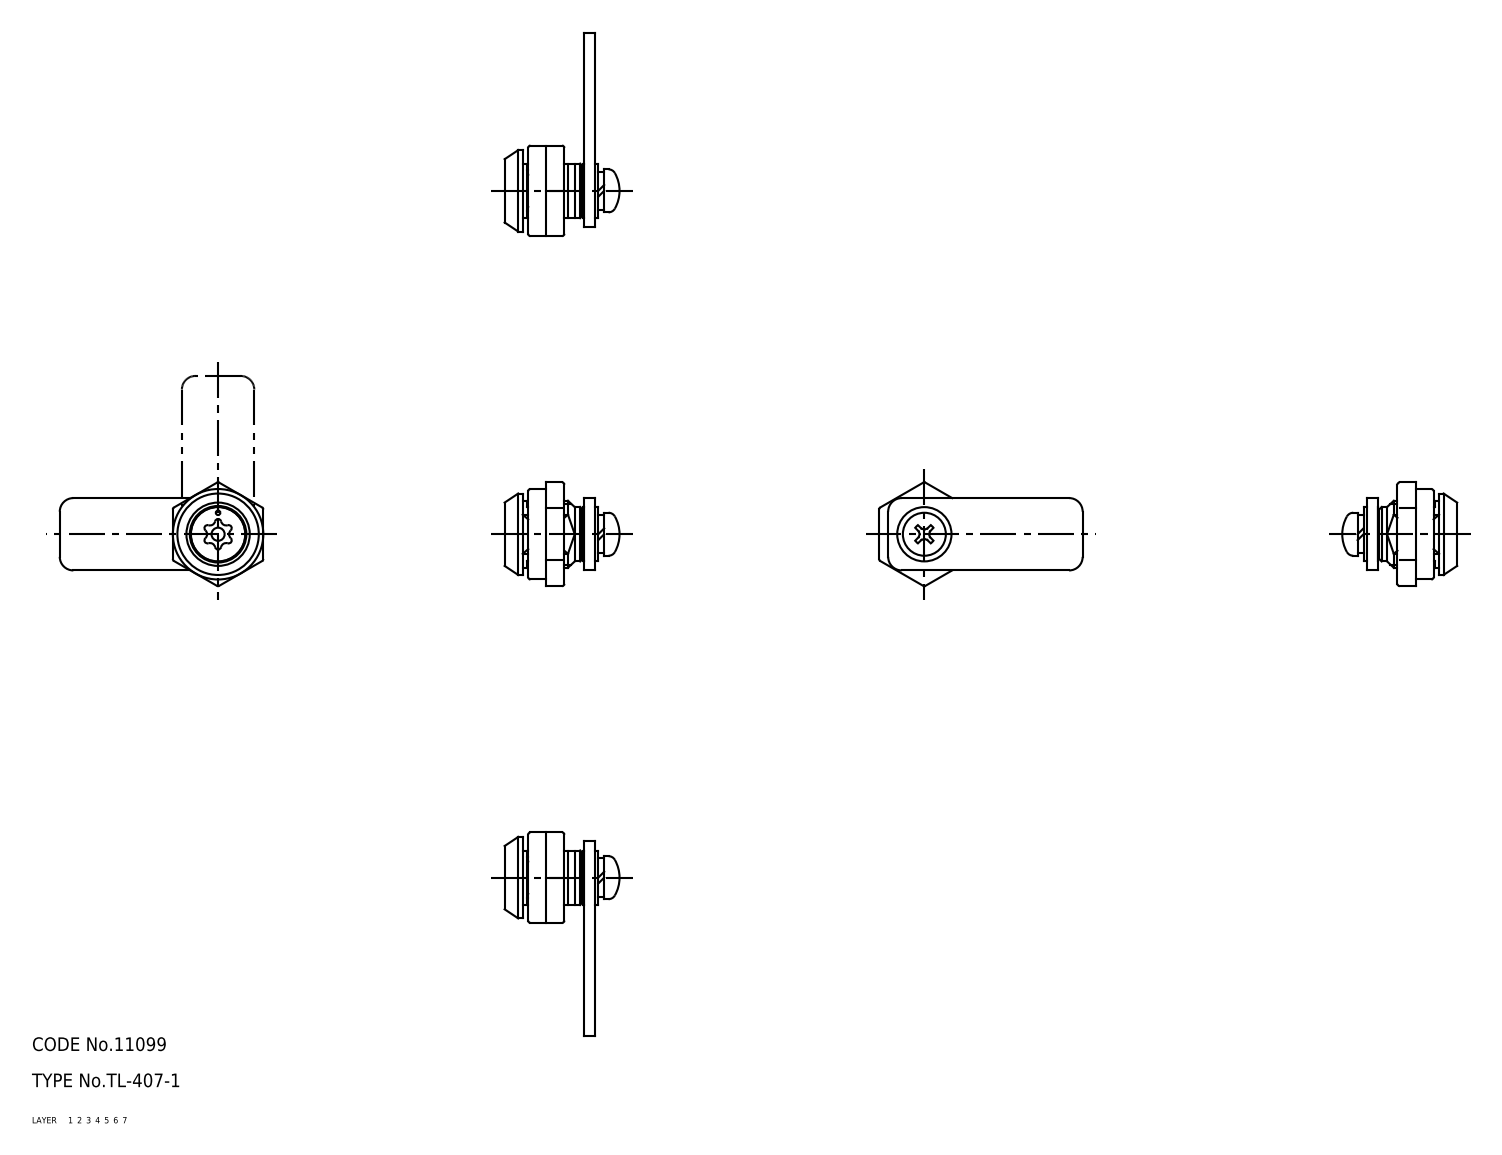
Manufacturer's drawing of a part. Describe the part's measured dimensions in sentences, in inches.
The part is named "plug; cam; case; nut (+2 more)". Its 3-D file was written by "SolidWorks 2015 (AUTOMOTIVE_DESIGN)". It is 5 solids with 178 faces: 87 planar, 73 cylindrical and 18 other. Overall it measures 1.772 by 1 by 0.903 inches. Its volume is 0.349 cubic inches and its surface area 9.26 square inches. Round holes: 1 of diameter 0.039, 1 of diameter 0.197, 1 of diameter 0.358, 1 of diameter 0.476, 1 of diameter 0.591, 1 of diameter 0.63. Round bosses or shafts: 1 of diameter 0.787, 1 of diameter 0.709, 1 of diameter 0.472, 1 of diameter 0.374, 1 of diameter 0.354, 1 of diameter 0.335, 1 of diameter 0.096. Partial cylindrical surfaces (rounded edges, fillets, slot ends): 12 of radius 0.02, 6 of radius 0.026, 6 of radius 0.049, 4 of radius 0.118, 1 of radius 0.197, 1 of radius 0.256, 1 of radius 0.291. The main face-to-face distances are 0.091, 0.157, 0.098, 0.354, 0.079, 0.626, 0.63, 0.197, 0.272, 0.181. The hole center spacings are 0.187.
